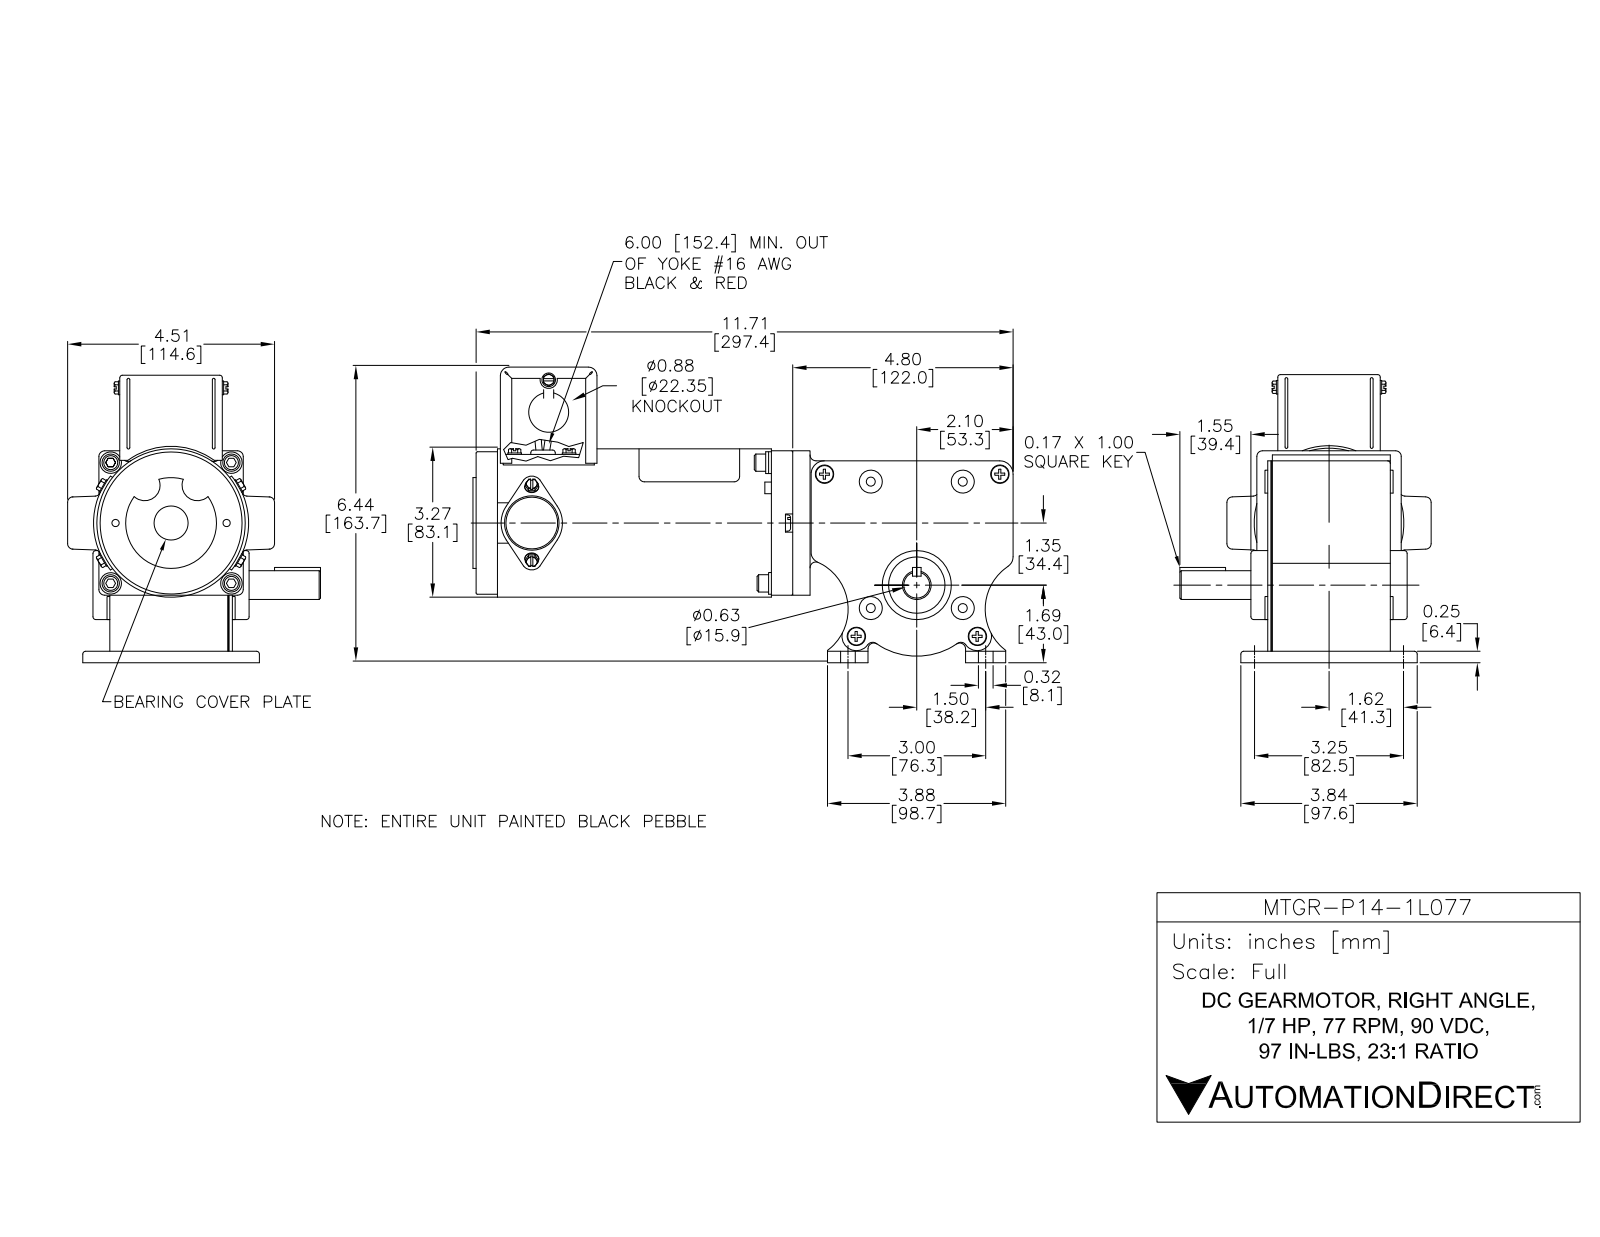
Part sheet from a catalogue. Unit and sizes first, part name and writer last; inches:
Units: inches
Overall size (bounding box): 11.791 × 6.522 × 5.415
Round holes (diameter × count): ⌀0.5 ×5, ⌀0.125 ×4, ⌀0.197 ×4, ⌀0.4 ×4, ⌀0.198 ×2, ⌀0.25 ×1, ⌀0.3 ×1, ⌀0.375 ×1, ⌀0.625 ×1, ⌀1 ×1, ⌀1.125 ×1, ⌀1.5 ×1
Round bosses / shafts (diameter × count): ⌀0.375 ×6, ⌀0.3 ×4, ⌀0.375 ×3, ⌀0.125 ×2, ⌀0.1 ×2, ⌀3.156 ×1, ⌀0.625 ×1, ⌀0.301 ×1
Partial cylindrical surfaces — rounded edges, fillets, slot ends (radius × count): R0.125 ×4, R0.16 ×4, R0.191 ×4, R0.234 ×4, R0.25 ×4, R0.13 ×2, R0.159 ×2, R0.29 ×2
Main face-to-face distances: 0.015, 0.03, 0.031, 2.603, 2.588, 2.573, 0.1, 0.07, 0.085, 2.673
Hole centre spacings: 1.318, 1.859, 2.63, 2.865, 1.118, 1.23, 2, 2.37
Volume: 64.64 in³ · Surface area: 475.7 in²
Bodies: 43 solids, 797 faces (486 planar, 283 cylindrical, 28 other)
Part name (STEP PRODUCT): P14-1L077
STEP written by: SolidWorks 2013 (AUTOMOTIVE_DESIGN)
